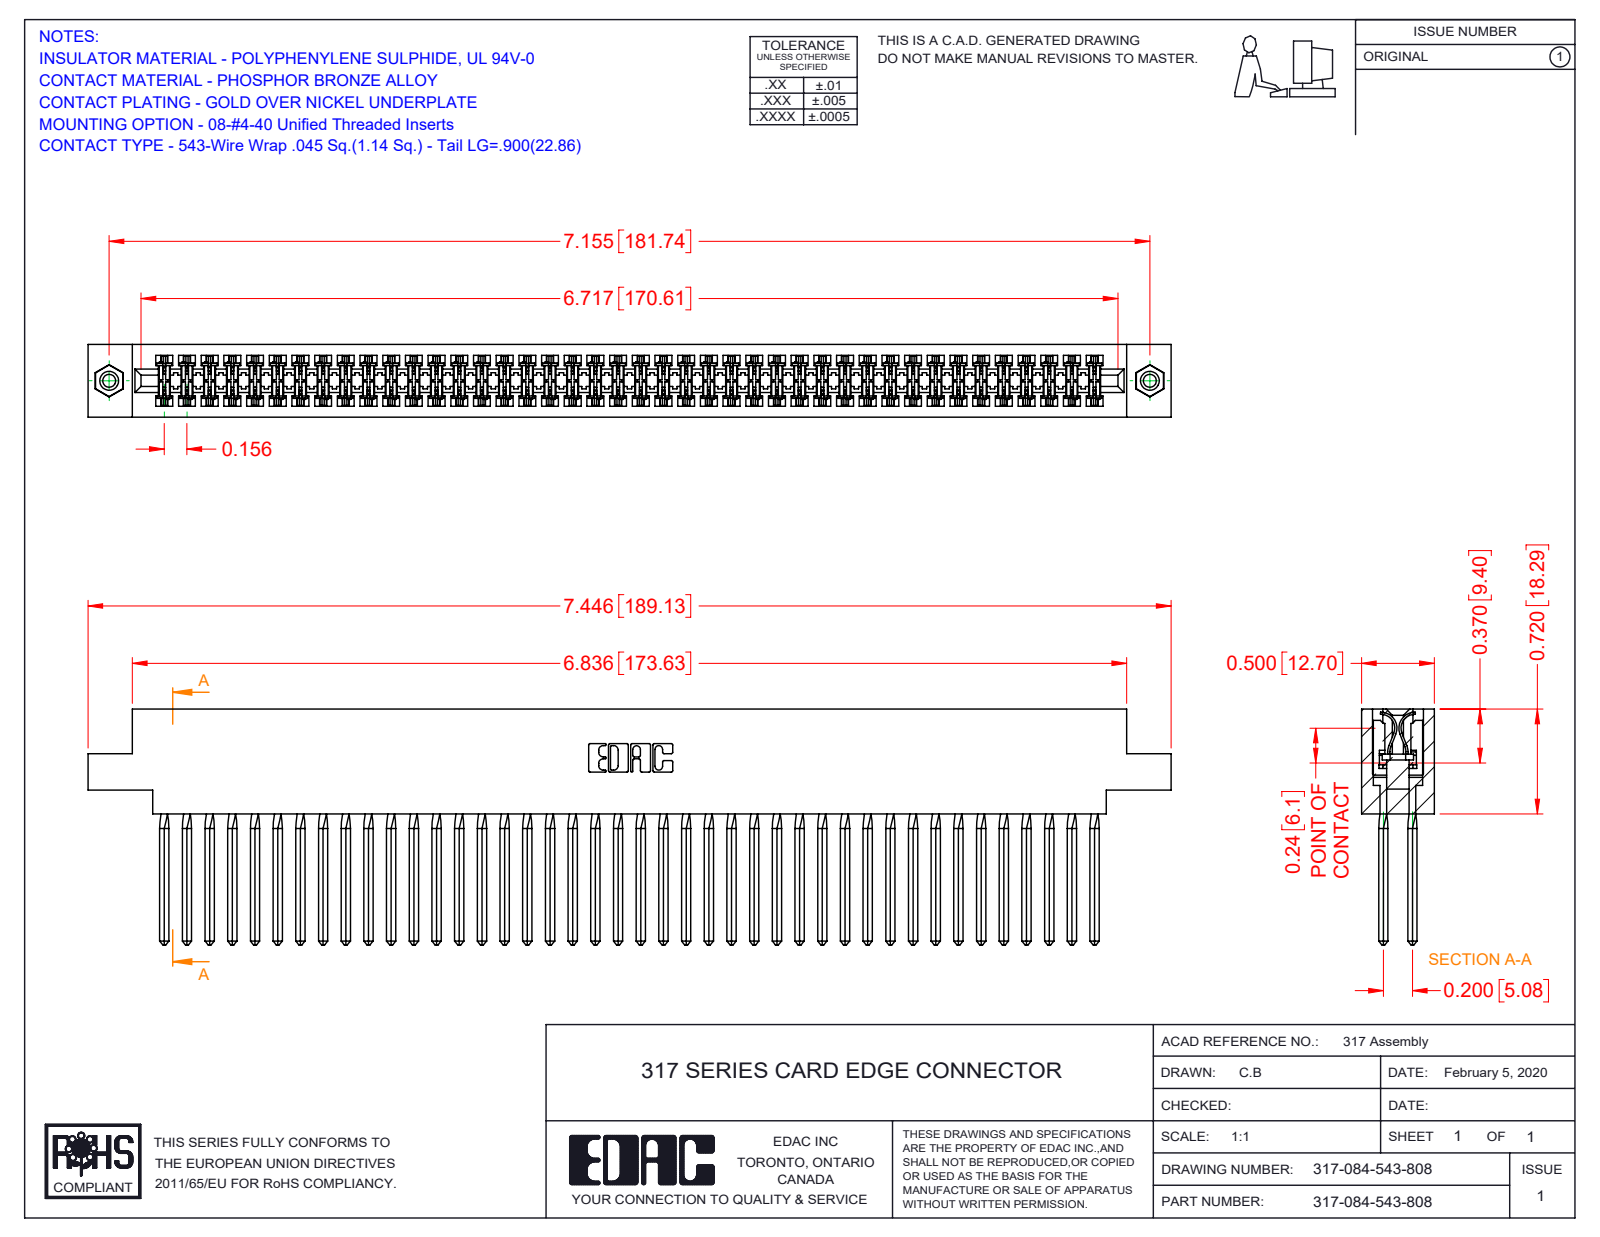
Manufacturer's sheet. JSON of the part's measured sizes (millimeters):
{"part_name": "345-250-001_345-250-003-102; 317 Part_.156 Dia - TI; 317-290-001_543; 317-084-543-878", "step_written_by": "SolidWorks 2016 (CONFIG_CONTROL_DESIGN)", "units": "millimeters", "bodies": {"solids": 87, "faces": 7638, "planar": 6222, "cylindrical": 1064, "other": 352}, "overall_size": [189.1, 41.1, 12.7], "volume_mm3": 32150, "surface_area_mm2": 48800, "round_holes": [[2.3, 2], [3.2, 2], [4, 2]], "round_bosses_or_shafts": [[3.9, 2]], "partial_cylinders_radius": [[0.4, 168], [0.3, 22], [0.2, 6], [0.8, 6], [0.7, 3], [2.4, 2], [2.5, 2], [2.8, 2]], "face_to_face_distances": [12.7, 1.9, 10.8, 8.9, 5, 2.8, 2.4, 5.1, 2.9, 3.3], "hole_center_spacings": [181.7]}
